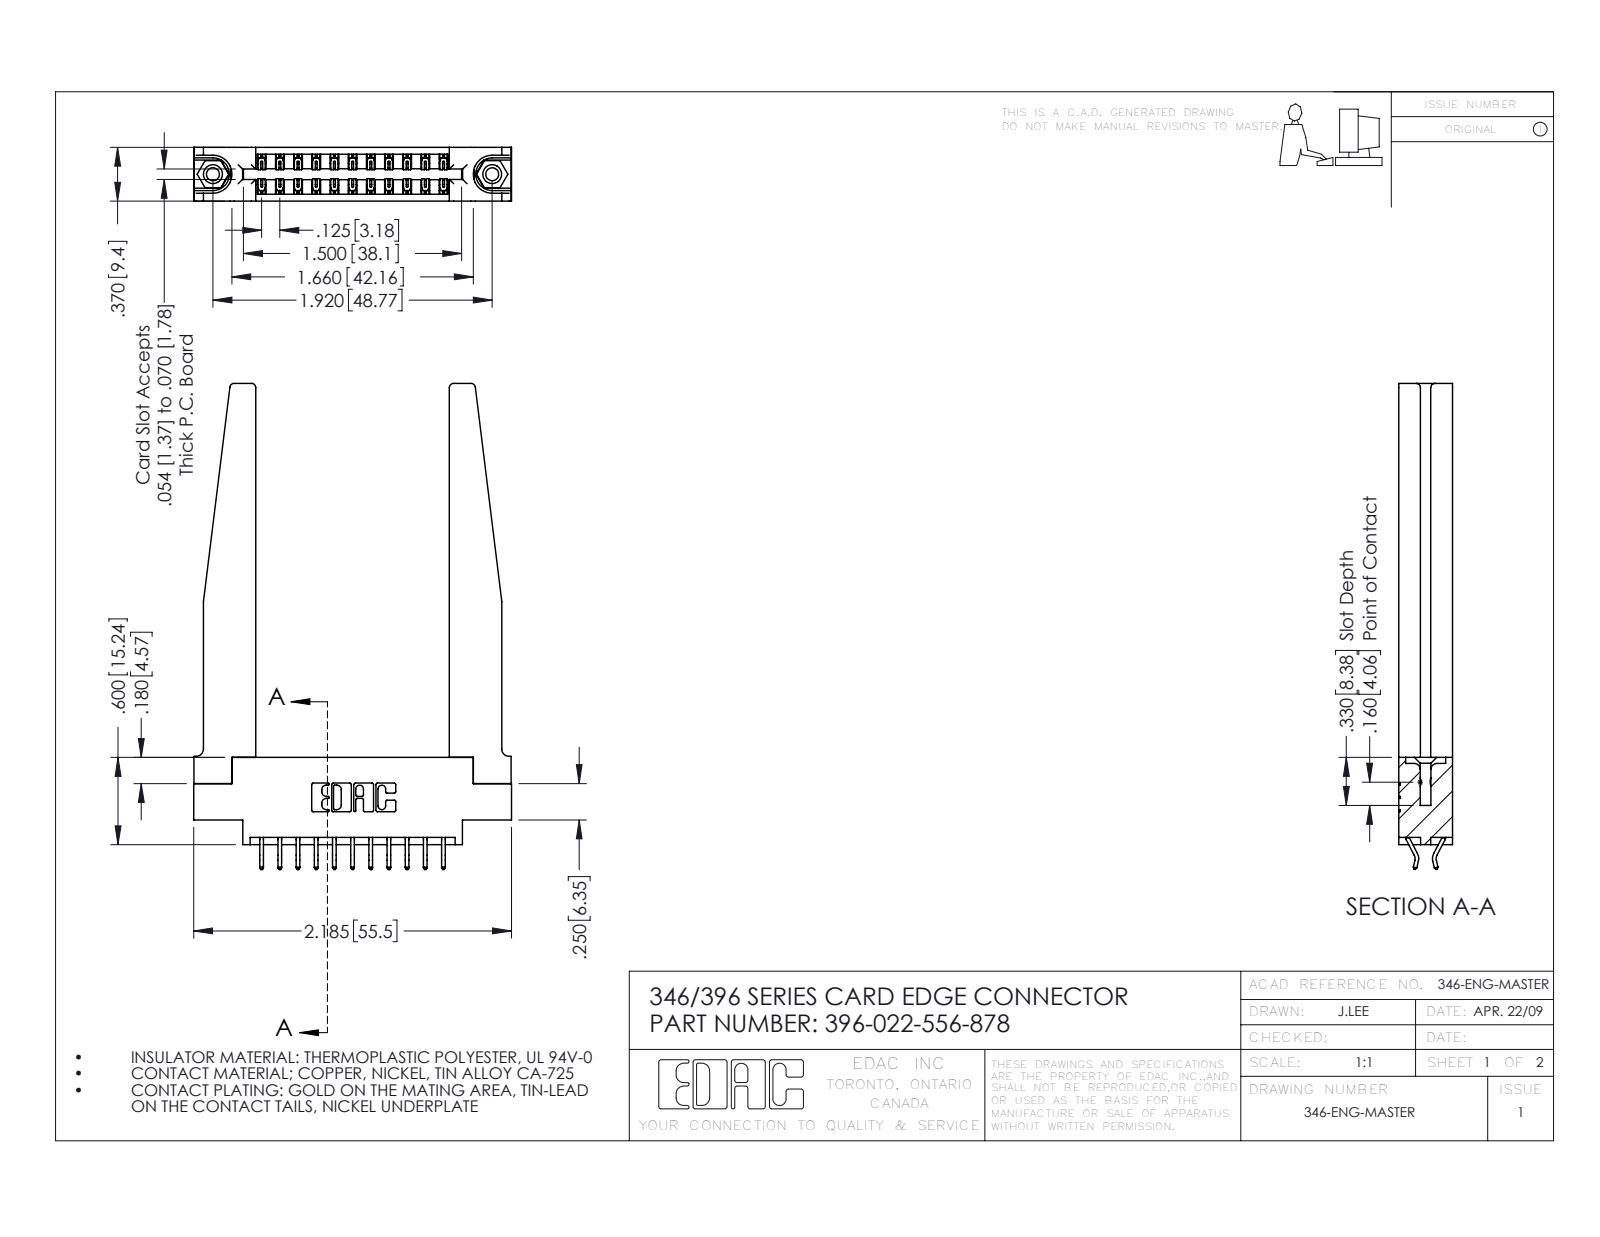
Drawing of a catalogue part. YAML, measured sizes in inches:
part_name: "346-220-078_345-220-078; 345-250-001_345-250-001-102; 396-022-556-878; 346 Part_0.170 Offset - 0.156 Dia-TH (+1 more)"
step_written_by: "SolidWorks 2016 (CONFIG_CONTROL_DESIGN)"
units: inches
bodies: {solids: 27, faces: 1636, planar: 1080, cylindrical: 504, other: 52}
overall_size: [3.34, 2.185, 0.37]
volume: 0.728
surface_area: 20.31
round_holes:
  - {diameter: 0.089, count: 2}
  - {diameter: 0.125, count: 2}
  - {diameter: 0.156, count: 2}
  - {diameter: 0.064, count: 1}
round_bosses_or_shafts:
  - {diameter: 0.155, count: 2}
partial_cylinders:
  - {radius: 0.006, count: 33}
  - {radius: 0.01, count: 22}
  - {radius: 0.03, count: 8}
  - {radius: 0.007, count: 6}
  - {radius: 0.031, count: 6}
  - {radius: 0.05, count: 4}
  - {radius: 0.026, count: 3}
  - {radius: 0.01, count: 2}
face_to_face_distances: [0.37, 0.15, 0.072, 0.148, 0.048, 0.322, 0.102, 0.22, 0.173, 0.25]
hole_center_spacings: [0.246, 1.715, 1.92]
